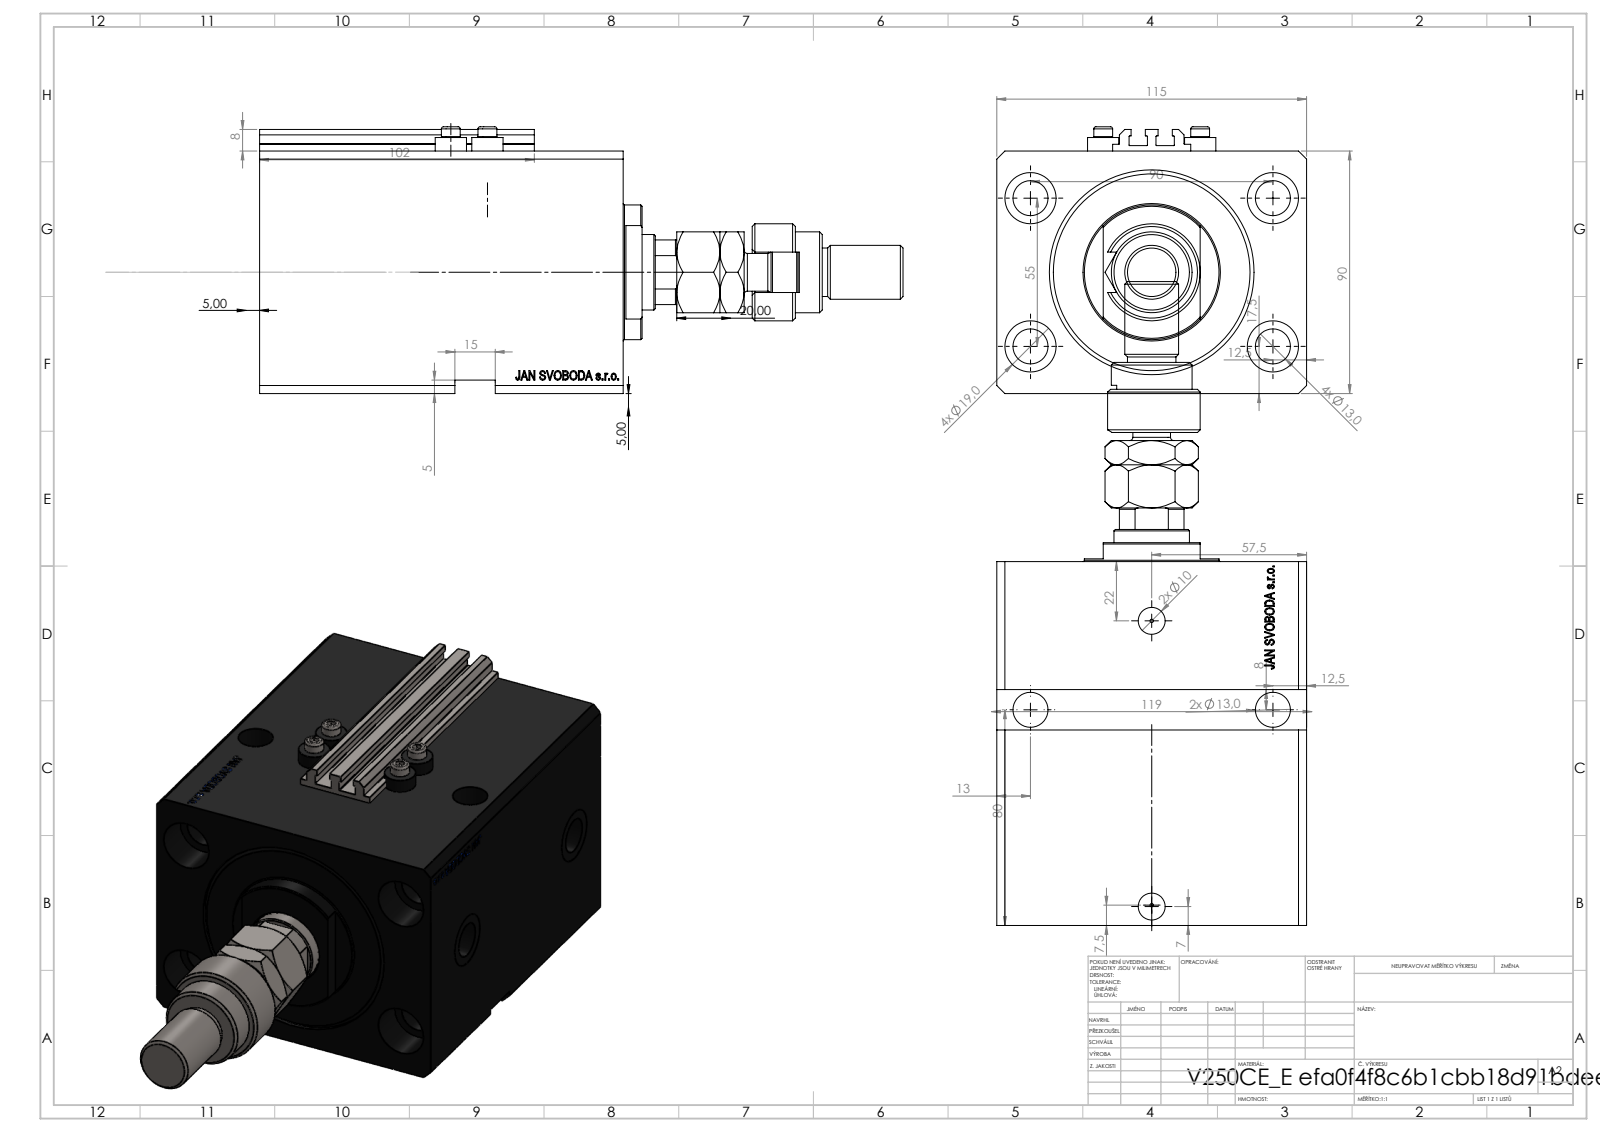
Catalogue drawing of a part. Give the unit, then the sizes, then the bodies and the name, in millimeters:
Units: millimetres
Overall size (bounding box): 238.9 × 115 × 99
Round holes (diameter × count): ⌀13 ×6, ⌀1.25 ×4, ⌀4 ×4, ⌀19 ×4, ⌀10 ×2, ⌀13.16 ×2, ⌀20 ×2, ⌀18.5 ×1, ⌀28 ×1, ⌀63 ×1, ⌀76 ×1
Round bosses / shafts (diameter × count): ⌀11.6 ×4, ⌀7 ×4, ⌀50 ×1, ⌀36 ×1, ⌀30 ×1, ⌀22 ×1, ⌀20 ×1, ⌀18 ×1
Partial cylindrical surfaces — rounded edges, fillets, slot ends (radius × count): R0.2 ×10, R7.5 ×1, R12 ×1, R13.5 ×1
Main face-to-face distances: 90, 115, 135, 87, 17.9, 117.1, 104.9, 30.1, 50, 54.9
Hole centre spacings: 52.74, 90, 13.6, 27.39, 28.46, 33.62, 36, 38.48
Volume: 1 226 000 mm³ · Surface area: 198 324 mm²
Bodies: 10 solids, 1192 faces (571 planar, 139 cylindrical, 482 other)
Part name (STEP PRODUCT): V250CE_E_Body; V250CE_VC_E; FEMALE_PART_FOR_DFA; MFA (+2 more)
STEP written by: SolidWorks 2019 (CONFIG_CONTROL_DESIGN)
